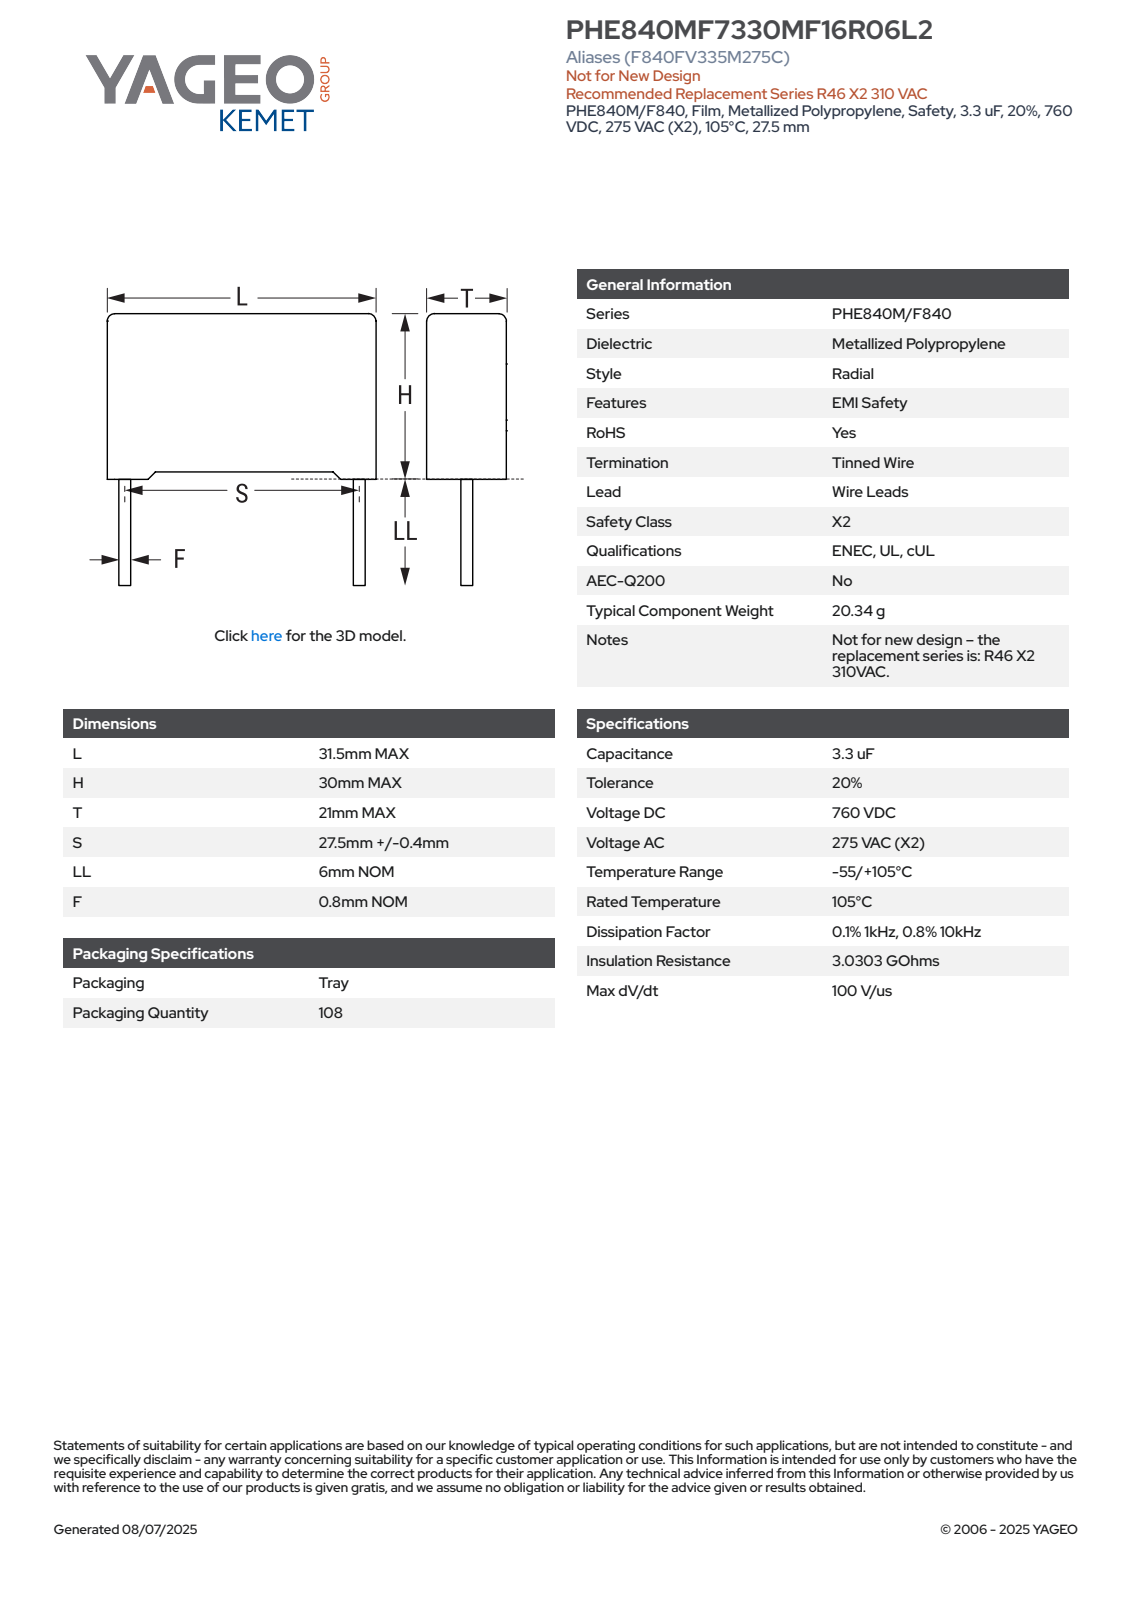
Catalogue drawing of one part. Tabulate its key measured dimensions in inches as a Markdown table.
| quantity | value |
| --- | --- |
| part name | CFR_RB2_31.5X30X21_L31.5H30T21S27.5LL6F0.8 |
| STEP written by | SolidWorks 2021 (AUTOMOTIVE_DESIGN) |
| units | inches |
| bodies | 4 solids, 85 faces (77 planar, 8 cylindrical, 0 other) |
| overall size | 1.417 × 1.24 × 0.827 |
| volume | 1.175 in³ |
| surface area | 7.057 in² |
| round bosses / shafts (diameter × count) | 0.031 × 2 |
| partial cylindrical surfaces (radius × count) | 0.02 × 4 |
| main face-to-face distances | 0.827, 1.24, 1.141, 1.152, 0.03, 0.041, 1.181, 0.041, 1.199, 0.827 |
